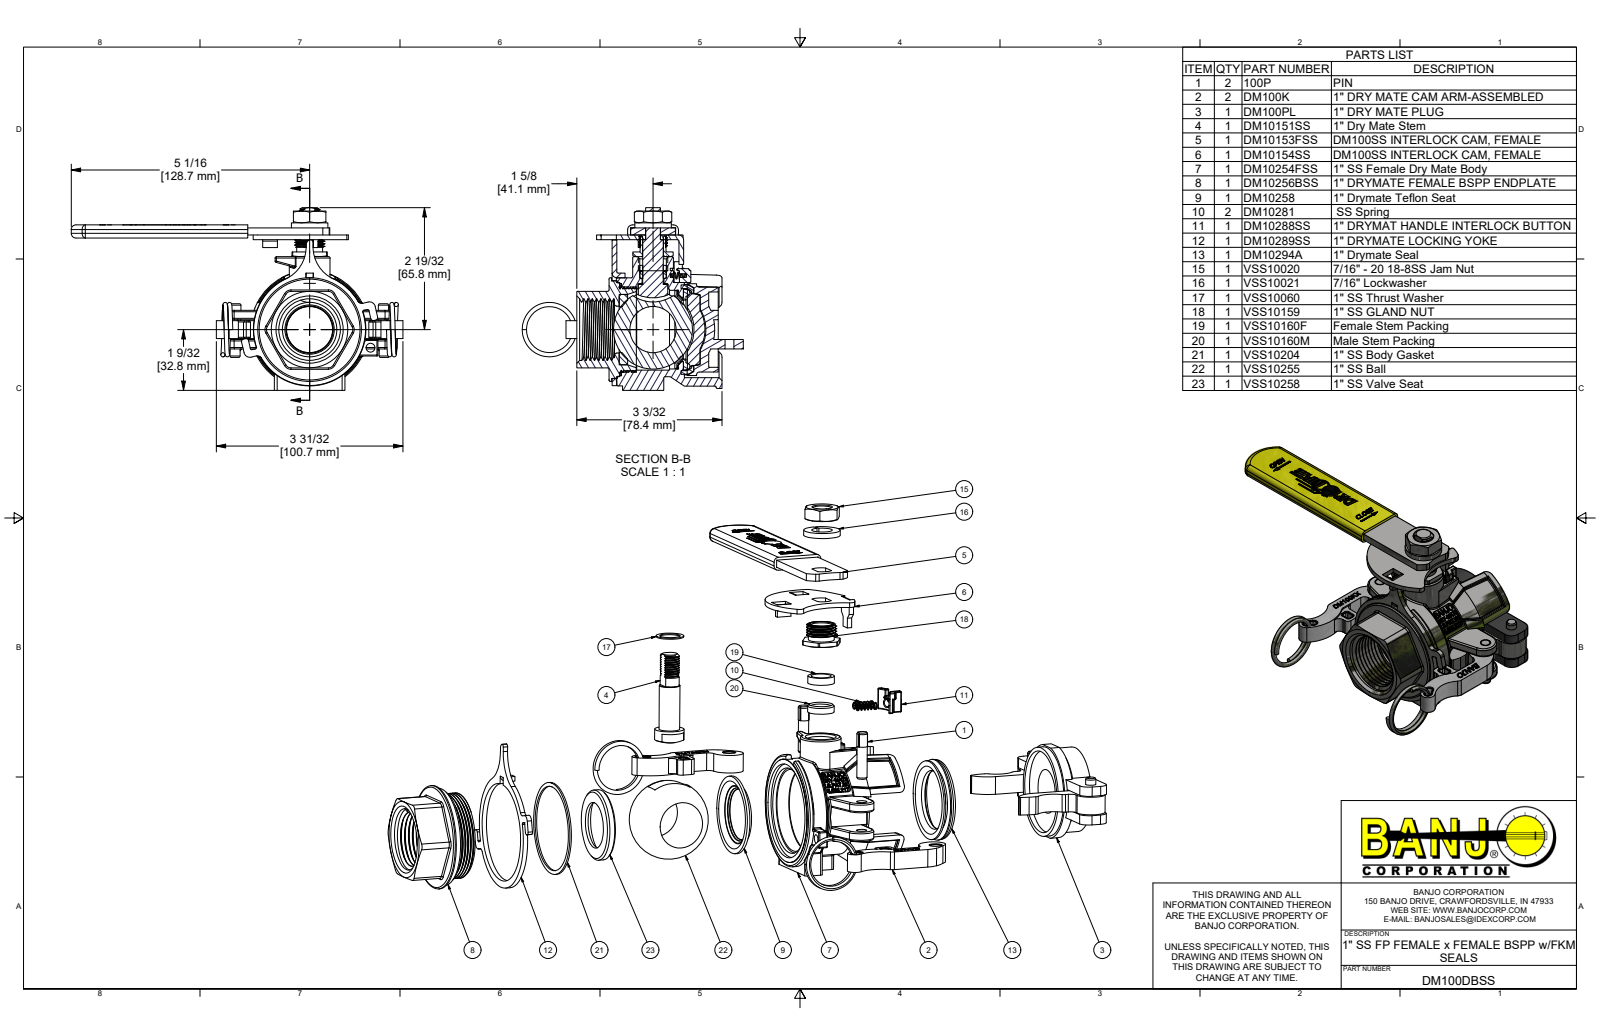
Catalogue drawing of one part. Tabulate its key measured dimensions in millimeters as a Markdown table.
| quantity | value |
| --- | --- |
| part name | DM100DBSS; DM10151SS; DM10281; VSS10020 (+8 more) |
| STEP written by | Autodesk Inventor 2022 (AUTOMOTIVE_DESIGN) |
| units | millimeters |
| bodies | 37 solids, 2918 faces (1244 planar, 628 cylindrical, 1046 other) |
| overall size | 179 × 119.3 × 98.5 |
| volume | 198 900 mm³ |
| surface area | 127 800 mm² |
| round holes (diameter × count) | 3.2 × 3, 5.5 × 2, 5.6 × 2, 5.7 × 2, 5.8 × 2, 6.2 × 2, 4.7 × 1, 4.8 × 1, 9.7 × 1, 11 × 1, 11 × 1, 11.1 × 1 |
| round bosses / shafts (diameter × count) | 5.8 × 4, 5.5 × 4, 5.6 × 3, 0.3 × 2, 60.7 × 1, 55.9 × 1, 52.6 × 1, 50.8 × 1 |
| partial cylindrical surfaces (radius × count) | 0.8 × 69, 0.4 × 50, 0.5 × 27, 2.5 × 21, 3.2 × 14, 1 × 8, 1.5 × 8, 2.3 × 8 |
| main face-to-face distances | 1.7, 3.9, 5.5, 1.5, 3.8, 5.6, 15.2, 5.6, 5.1, 0.5 |
| hole center spacings | 15.8, 27.3, 20.2, 40.9, 42.2, 48.3, 52.8, 82.6 |
